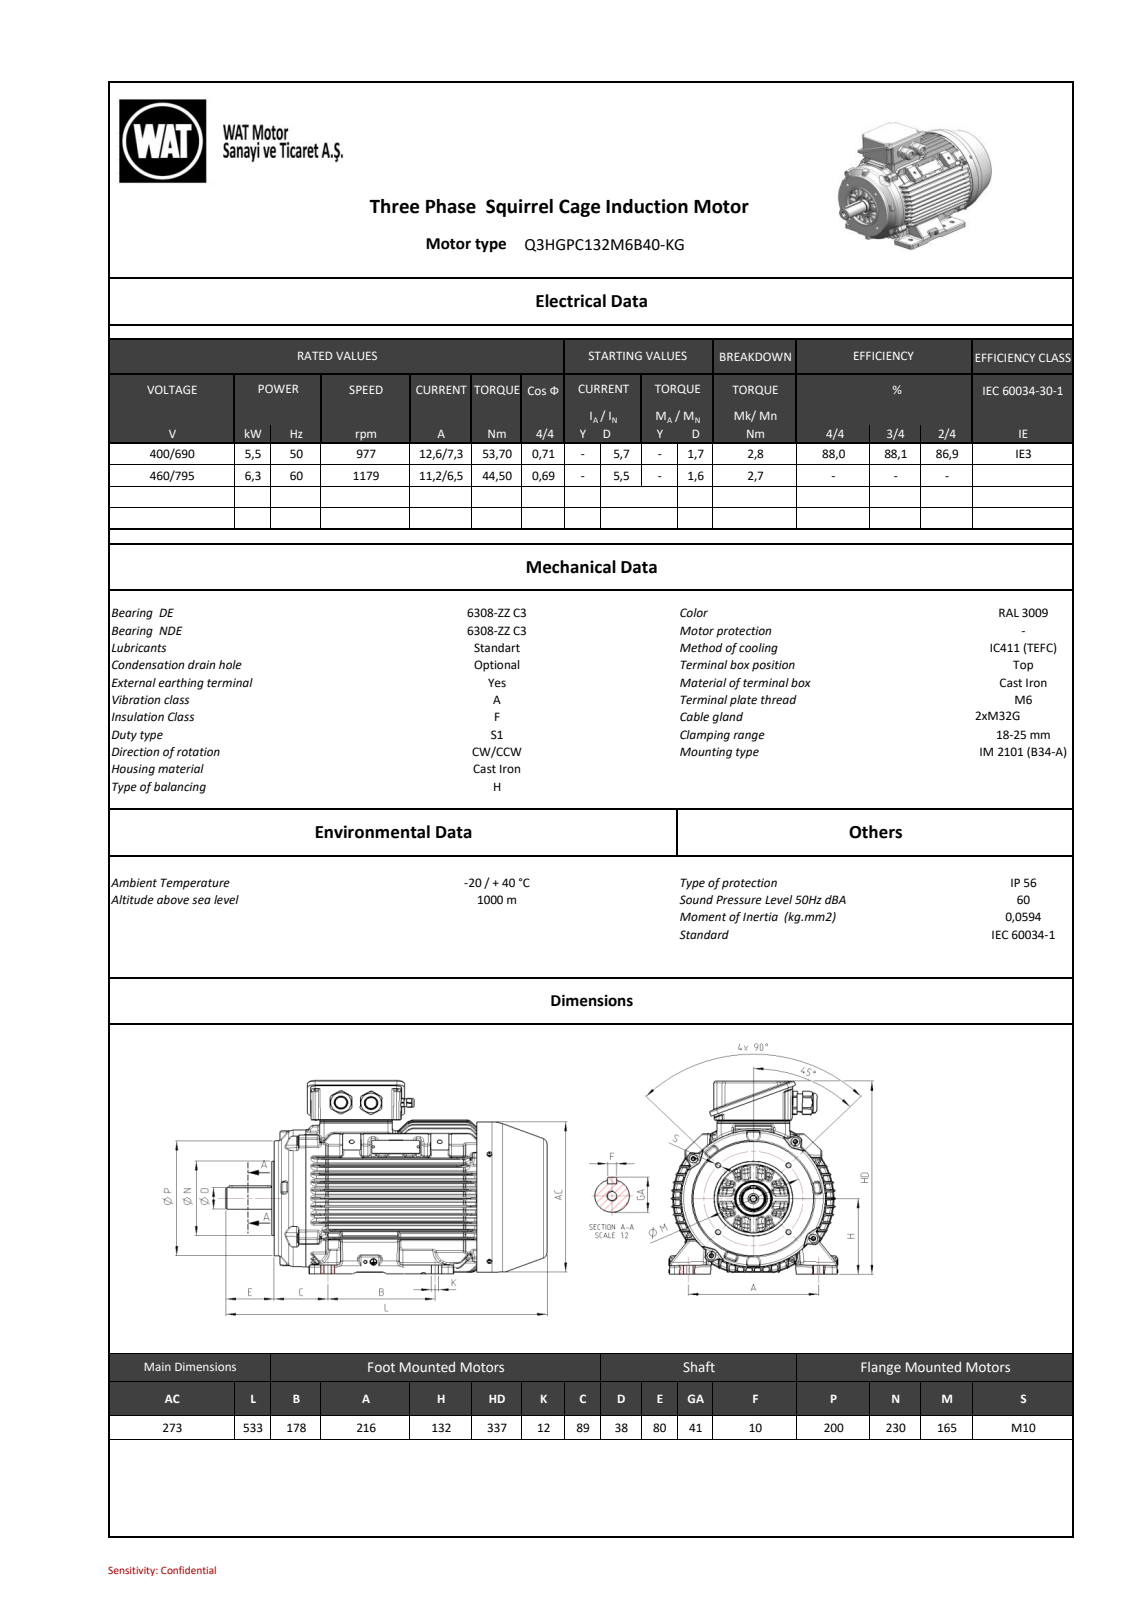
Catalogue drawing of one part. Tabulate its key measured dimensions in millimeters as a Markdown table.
| quantity | value |
| --- | --- |
| part name | 26000A30F4D8rono |
| STEP written by | SIEMENS PLM Software NX 11.0 (AUTOMOTIVE_DESIGN) |
| units | millimeters |
| bodies | 0 solids, 6111 faces (1123 planar, 1706 cylindrical, 3282 other) |
| overall size | 533 × 337.41 × 279.6 |
| round holes (diameter × count) | 5.5 × 8, 6.8 × 8, 8.5 × 8, 4.2 × 3, 2.5 × 2, 19 × 2, 21 × 2, 5 × 1, 10.3 × 1, 13 × 1, 34.2 × 1, 58.4 × 1 |
| round bosses / shafts (diameter × count) | 13 × 4, 8.65 × 4, 8 × 4, 36 × 2, 34.5 × 2, 31.25 × 2, 14.8 × 2, 267 × 1 |
| partial cylindrical surfaces (radius × count) | 4 × 299, 3 × 178, 1.5 × 106, 2 × 75, 1.8 × 50, 6 × 36, 1 × 35, 26 × 24 |
| main face-to-face distances | 13.76, 13.83, 27.59, 110.18, 82.59, 96.35, 55.94, 27.73, 41.49, 13.9 |
| hole center spacings | 136, 42.73, 121.5, 134.49, 158.28, 171.83, 203.26, 123.22 |
